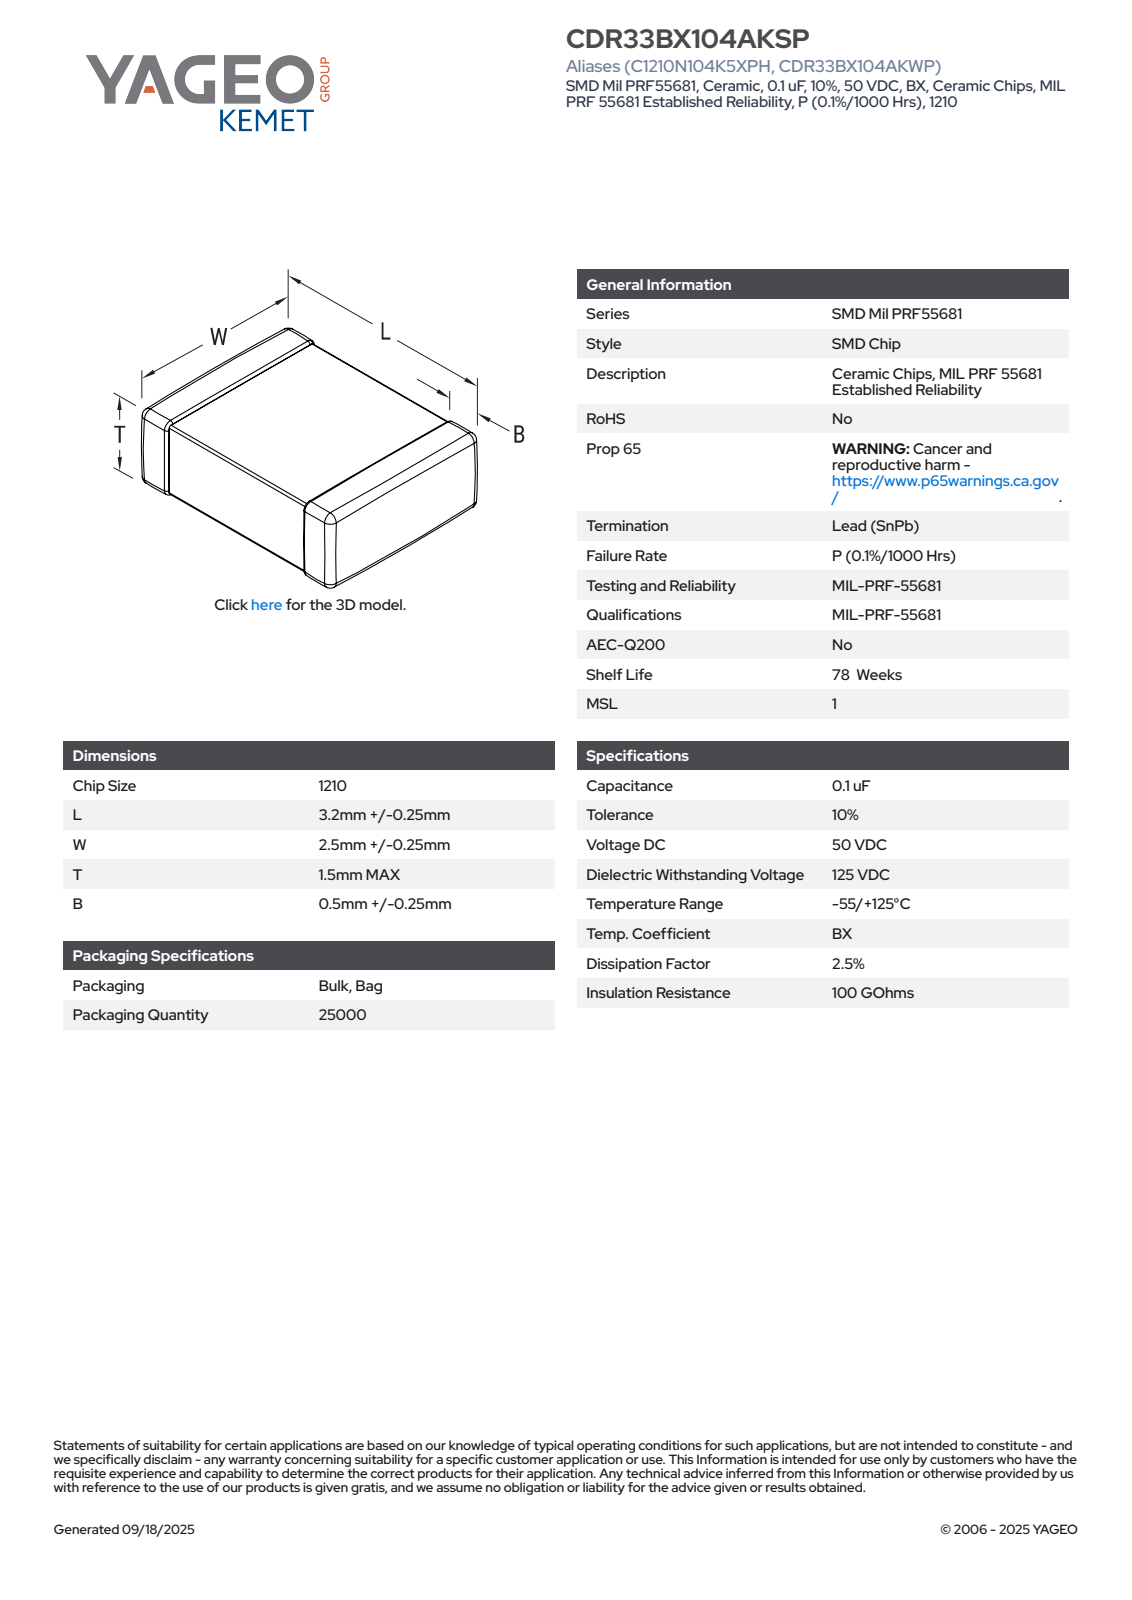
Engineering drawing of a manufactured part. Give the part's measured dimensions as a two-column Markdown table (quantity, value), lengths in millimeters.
| quantity | value |
| --- | --- |
| part name | CCS_STDNOS_1210_L2.2W1.45T1.3B0.5 |
| STEP written by | SolidWorks 2021 (AUTOMOTIVE_DESIGN) |
| units | millimeters |
| bodies | 4 solids, 125 faces (71 planar, 38 cylindrical, 16 other) |
| overall size | 2.2 × 1.45 × 1.3 |
| volume | 4 mm³ |
| surface area | 16 mm² |
| main face-to-face distances | 1.27, 1.42, 2.2, 1.3, 1.45, 1.24, 1.39, 0.7, 0.72, 0.75 |
